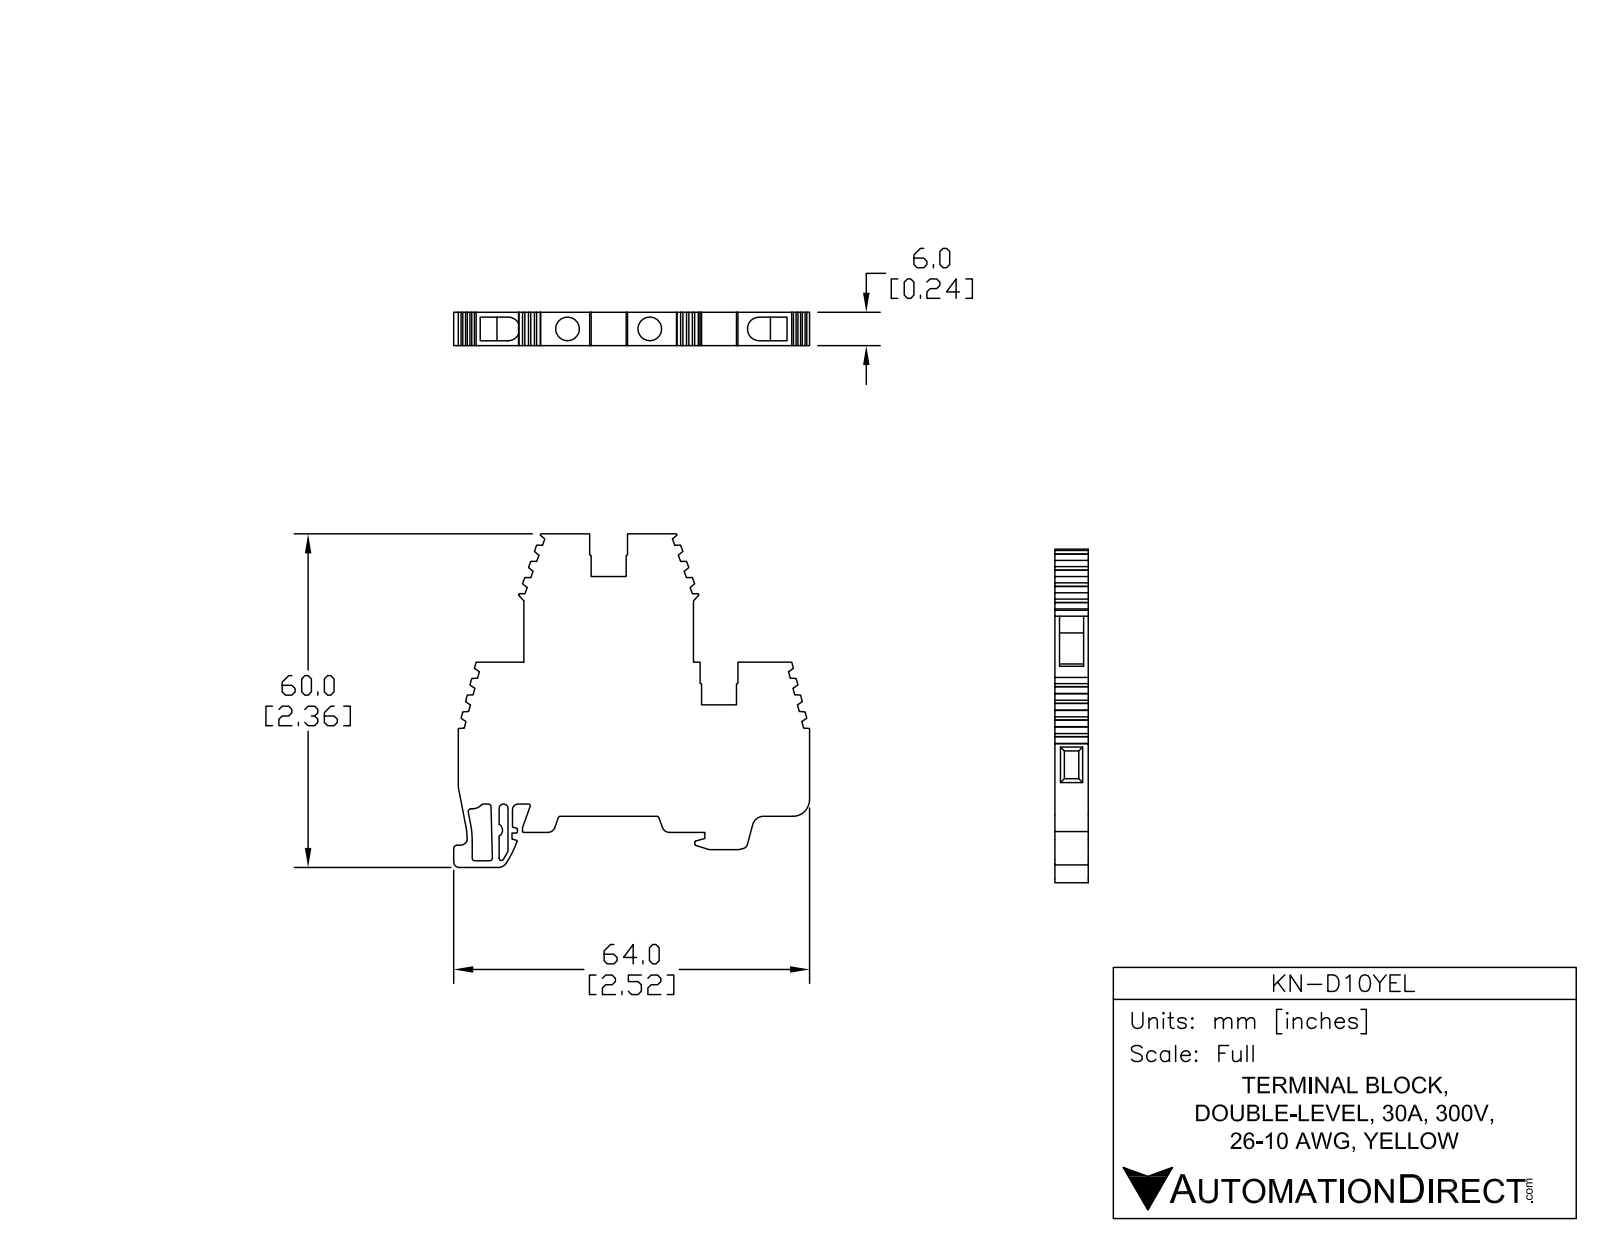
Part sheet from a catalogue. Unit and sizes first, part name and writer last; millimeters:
Units: millimetres
Overall size (bounding box): 64 × 60 × 6
Round holes (diameter × count): ⌀4.2 ×2
Partial cylindrical surfaces — rounded edges, fillets, slot ends (radius × count): R0.5 ×7, R0.3 ×6, R0.2 ×3, R1 ×3, R0.6 ×2, R2.1 ×2, R0.4 ×1, R0.8 ×1
Main face-to-face distances: 6, 2.9, 0.8, 5.2, 23.1, 6.6, 19.9, 6.3, 4, 5.9
Hole centre spacings: 14.8
Volume: 13 700 mm³ · Surface area: 7 432 mm²
Bodies: 1 solid, 235 faces (192 planar, 43 cylindrical, 0 other)
Part name (STEP PRODUCT): KN-D10GRY
STEP written by: SolidWorks 2015 (CONFIG_CONTROL_DESIGN)
